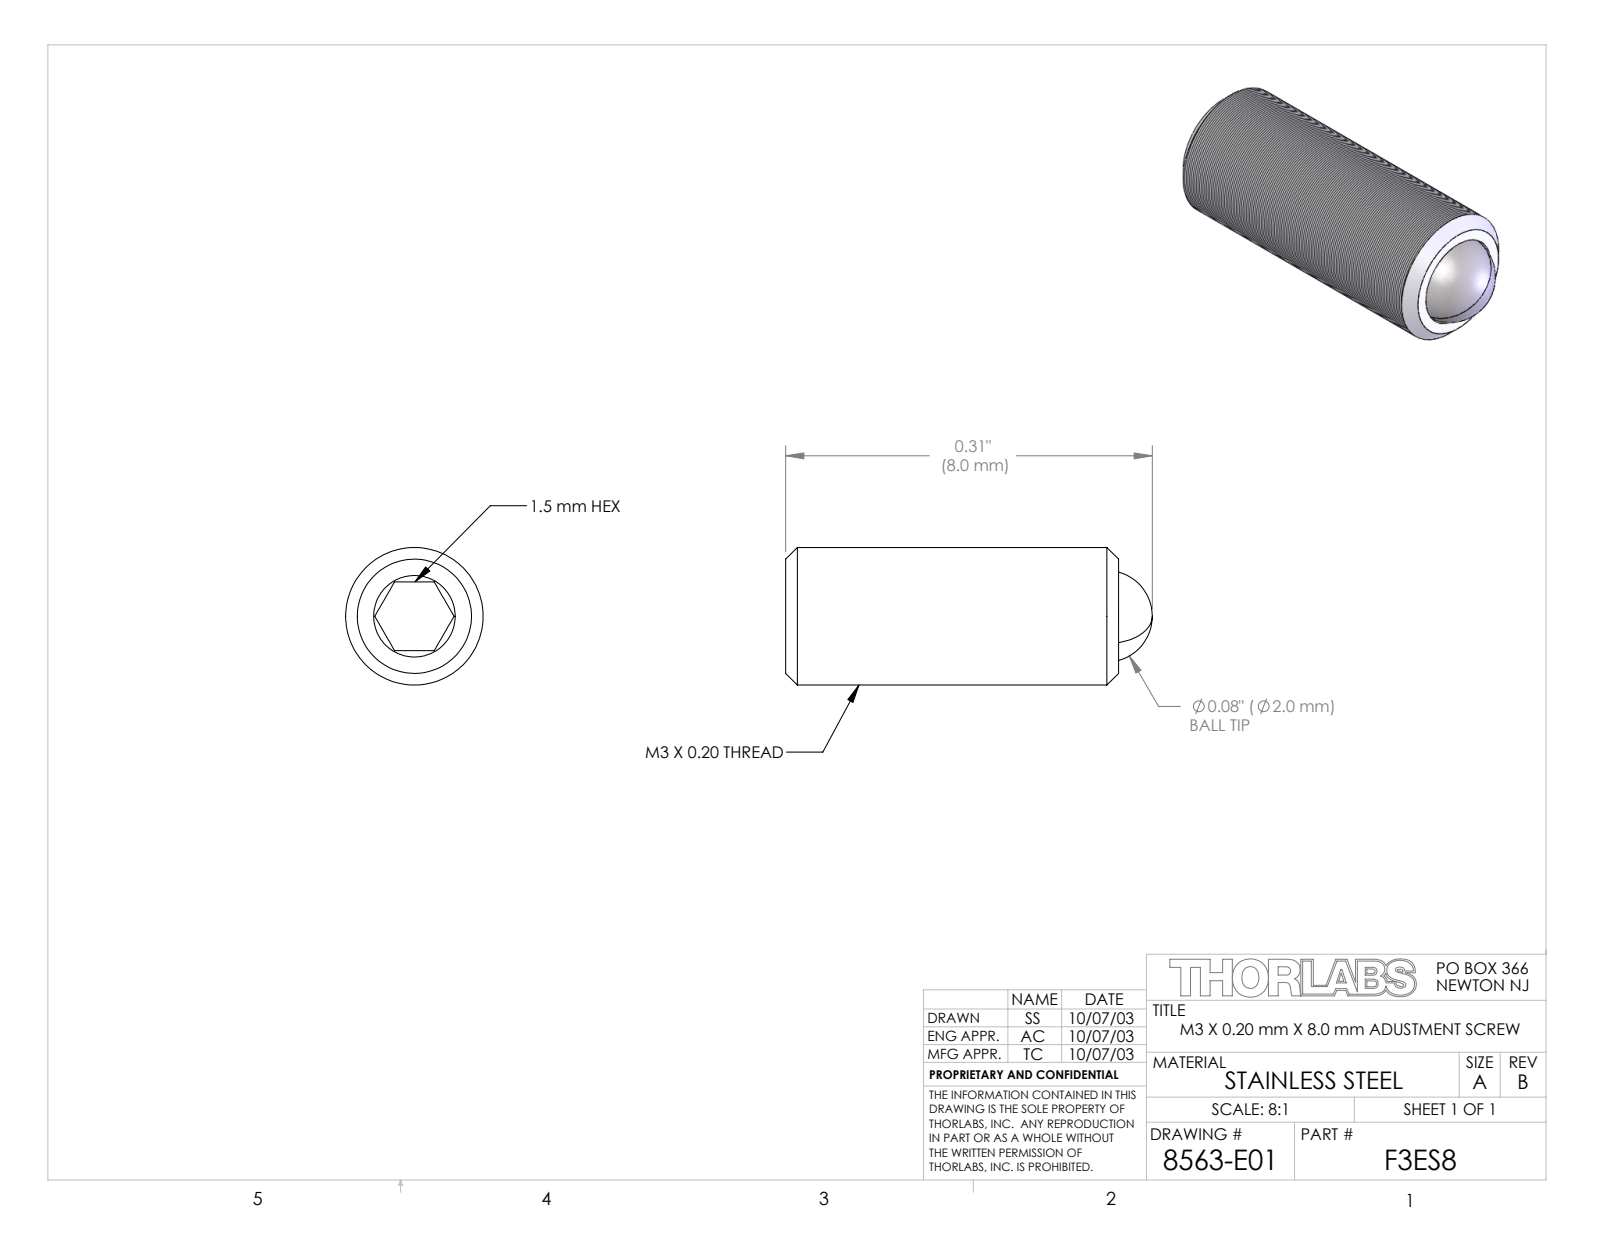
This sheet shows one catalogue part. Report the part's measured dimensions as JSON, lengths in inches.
{"part_name": "8563-E0W", "step_written_by": "SolidWorks 2014 (AUTOMOTIVE_DESIGN)", "units": "inches", "bodies": {"solids": 0, "faces": 20, "planar": 8, "cylindrical": 4, "other": 8}, "overall_size": [0.315, 0.118, 0.118], "round_holes": [[0.079, 1]], "round_bosses_or_shafts": [[0.118, 1]], "face_to_face_distances": [0.059, 0.286]}
